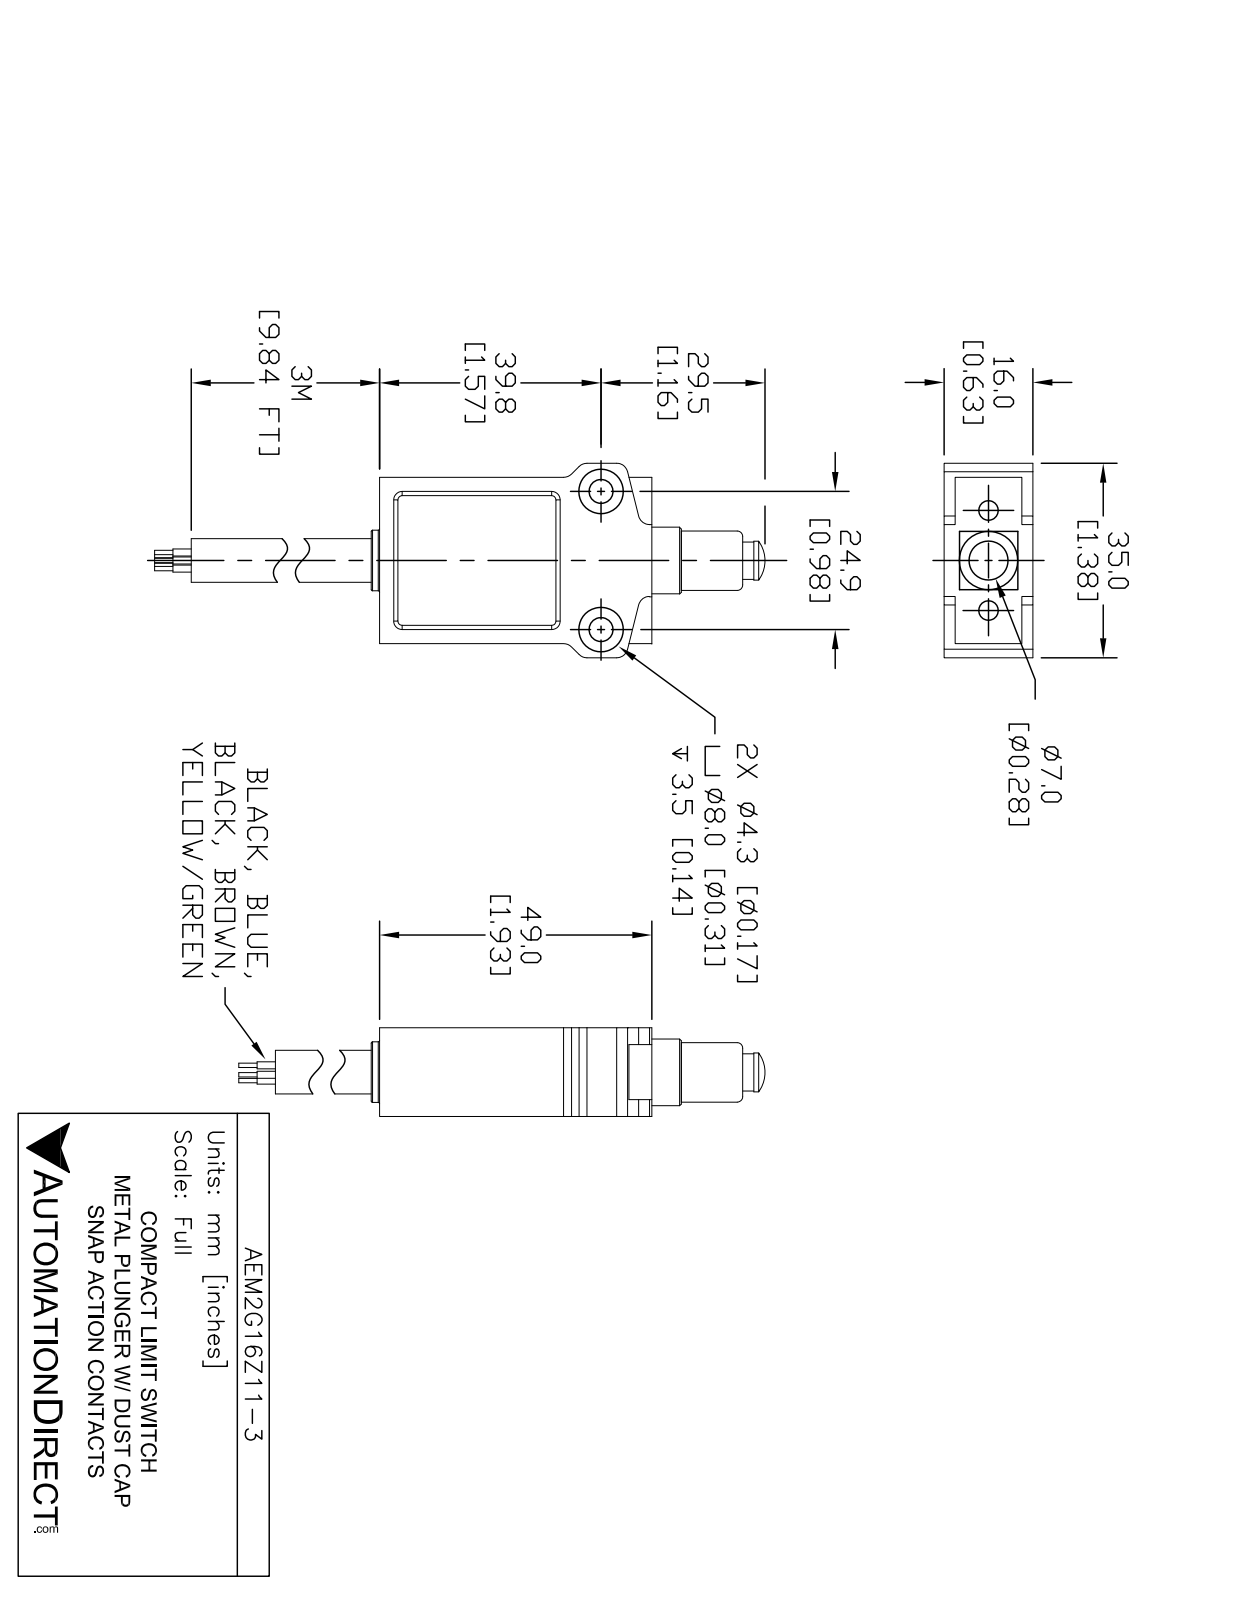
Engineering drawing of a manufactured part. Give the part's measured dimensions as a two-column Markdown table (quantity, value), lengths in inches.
| quantity | value |
| --- | --- |
| part name | AEM2G16Z11-3_Default |
| STEP written by | SolidWorks 2021 (CONFIG_CONTROL_DESIGN) |
| units | inches |
| bodies | 1 solid, 100 faces (43 planar, 40 cylindrical, 17 other) |
| overall size | 3.33 × 1.38 × 0.63 |
| volume | 1.444 in³ |
| surface area | 11.27 in² |
| round holes (diameter × count) | 0.177 × 2, 0.344 × 2 |
| round bosses / shafts (diameter × count) | 0.05 × 5, 0.031 × 5, 0.47 × 1, 0.43 × 1, 0.42 × 1, 0.31 × 1, 0.28 × 1, 0.26 × 1 |
| partial cylindrical surfaces (radius × count) | 0.03 × 8, 0.08 × 8 |
| main face-to-face distances | 0.03, 0.6, 0.57, 0.63, 1.18, 1.93, 0.187, 0.443, 0.157, 0.413 |
| hole center spacings | 0.98 |
